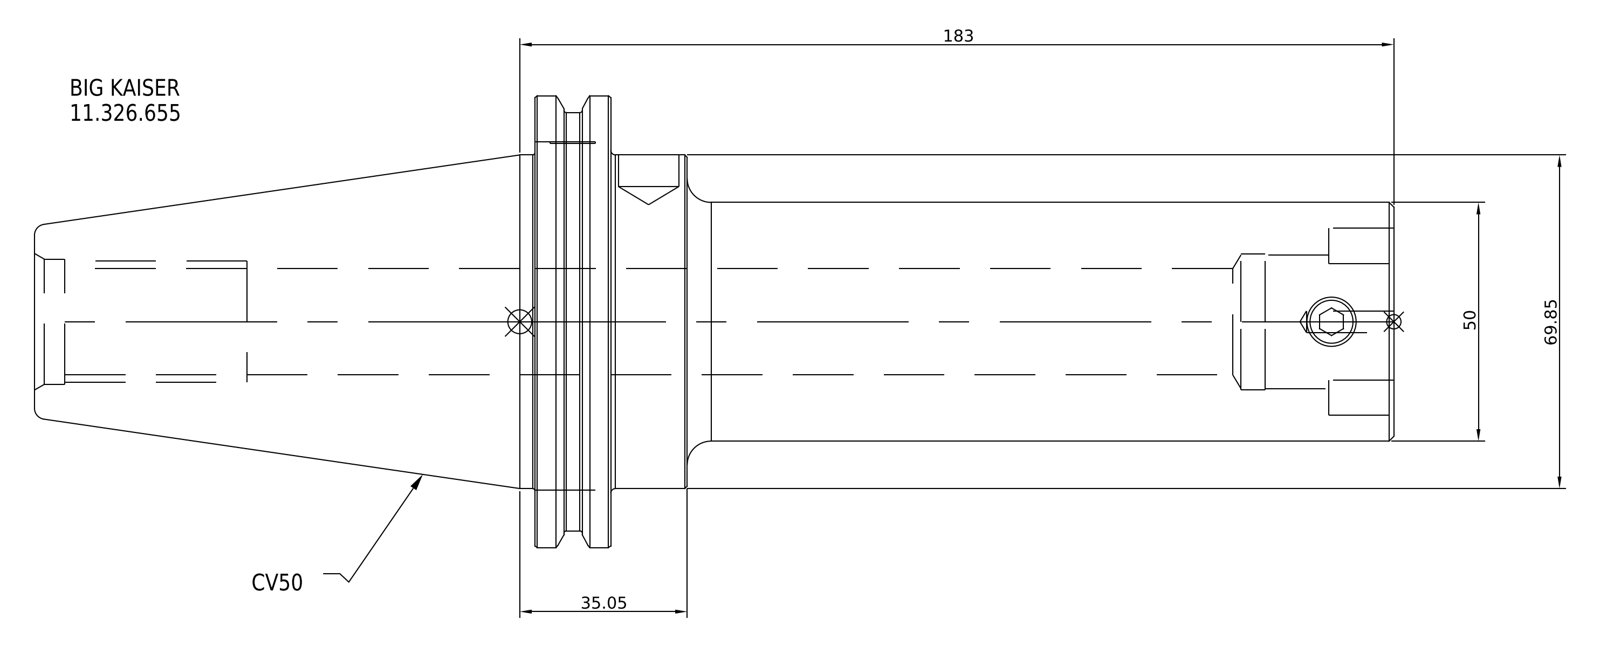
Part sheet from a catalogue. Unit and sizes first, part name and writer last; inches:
Units: inches
Overall size (bounding box): 11.205 × 3.875 × 3.875
Round bosses / shafts (diameter × count): ⌀3.875 ×1, ⌀3.594 ×1, ⌀2.75 ×1, ⌀1.969 ×1
Main face-to-face distances: 0.691, 6.455, 7.146, 5.827, 0.628, 1.319, 11.205, 5.378, 4.75, 4.059
Volume: 44.74 in³ · Surface area: 99.54 in²
Bodies: 1 solid, 16 faces (7 planar, 6 cylindrical, 3 other)
Part name (STEP PRODUCT): 11.326.655
STEP written by: SolidWorks 2021 (CONFIG_CONTROL_DESIGN)
